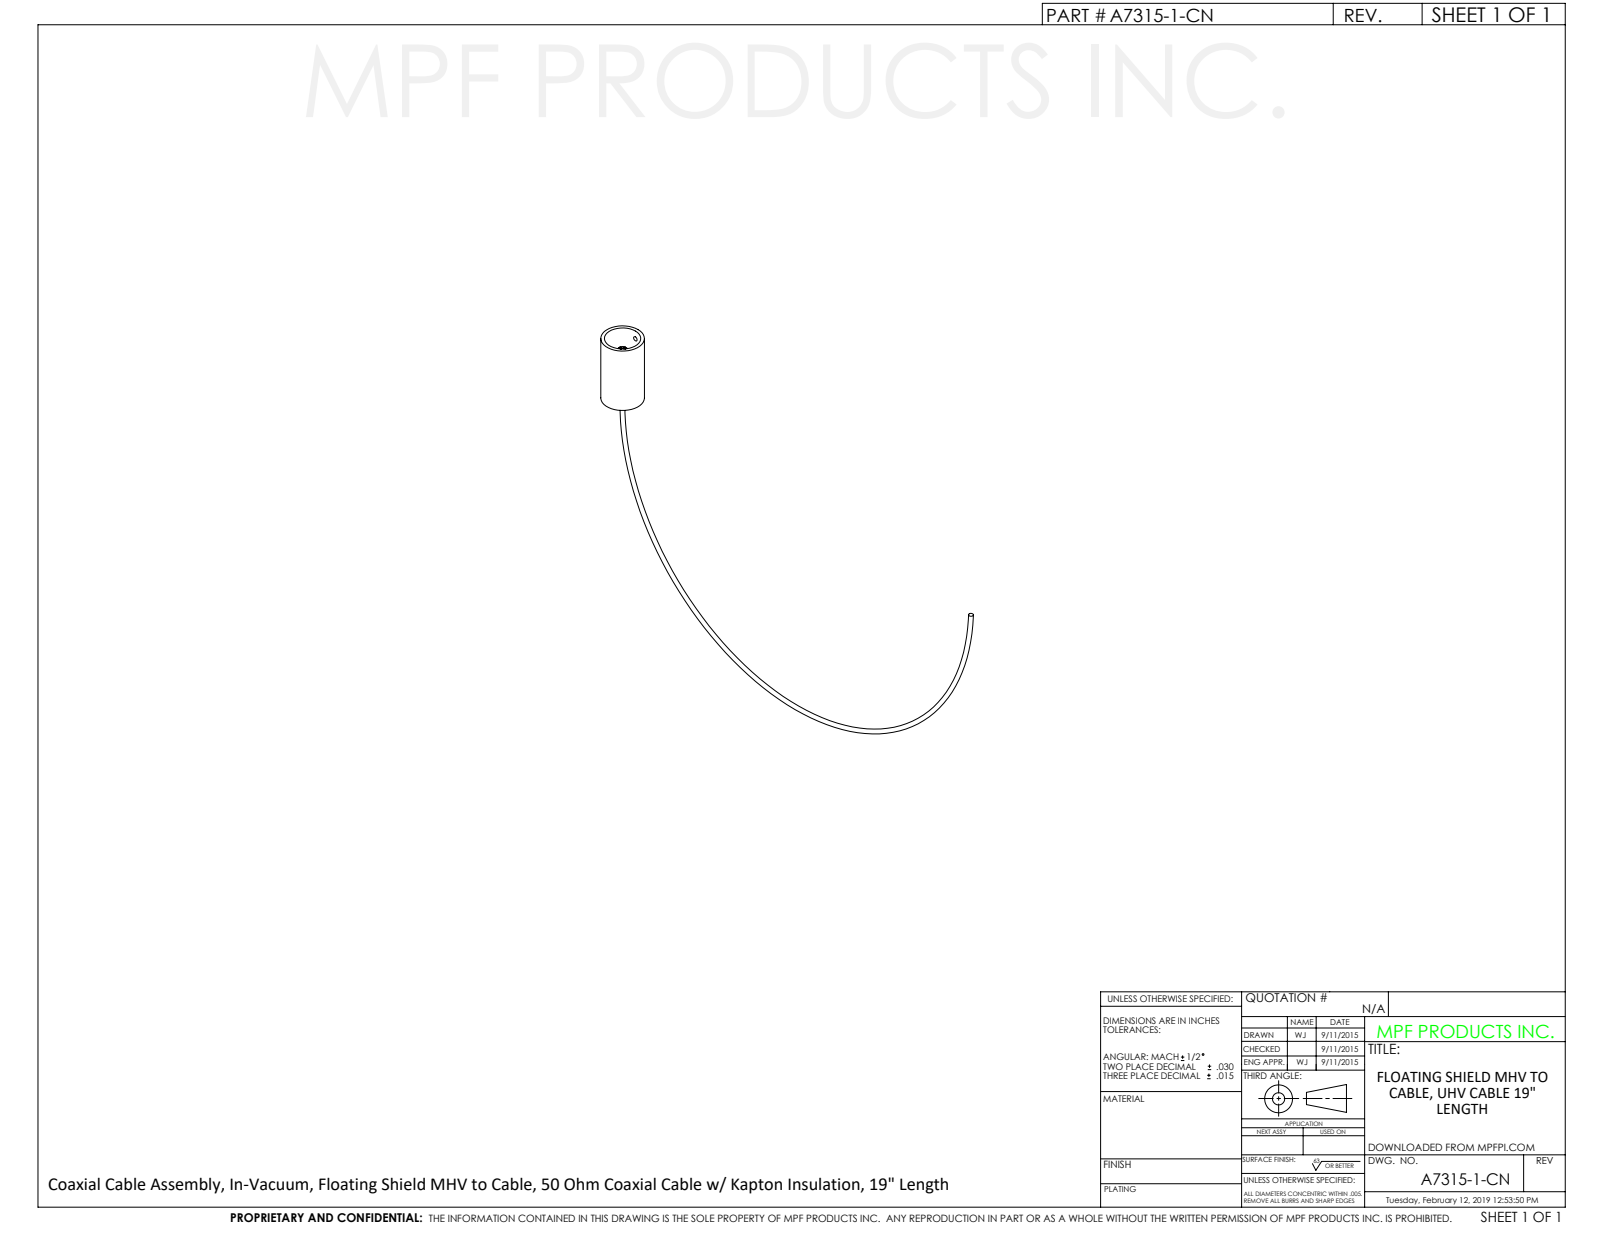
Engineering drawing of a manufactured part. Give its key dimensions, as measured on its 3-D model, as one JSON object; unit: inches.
{"part_name": "A7315-1-CN", "step_written_by": "SolidWorks 2012 (CONFIG_CONTROL_DESIGN)", "units": "inches", "bodies": {"solids": 1, "faces": 47, "planar": 22, "cylindrical": 20, "other": 5}, "overall_size": [10.712, 6.833, 1], "volume_in3": 0.992, "surface_area_in2": 13.71, "round_holes": [[0.1, 3], [0.2, 1], [0.75, 1]], "round_bosses_or_shafts": [[1, 1], [0.2, 1]], "face_to_face_distances": [1.5, 0.04, 0.02, 1.252, 0.248, 0.42, 0.38, 1.002, 0.25, 0.498], "hole_center_spacings": [0.35]}
